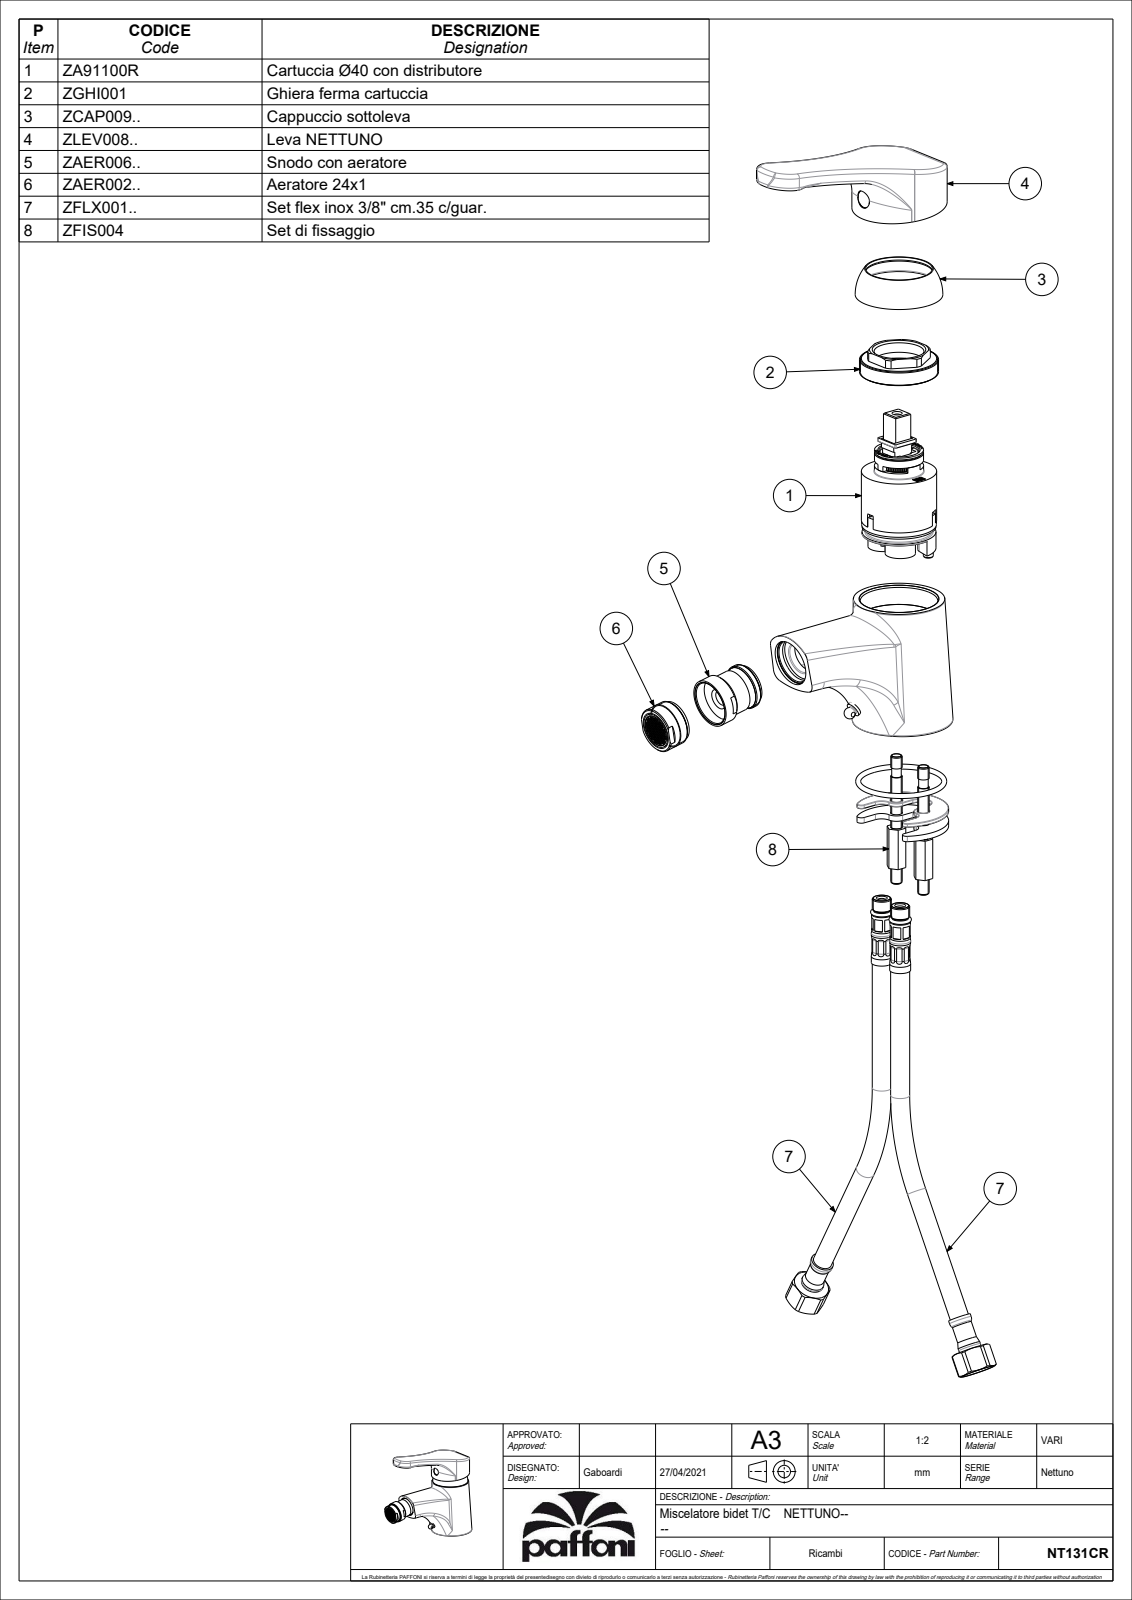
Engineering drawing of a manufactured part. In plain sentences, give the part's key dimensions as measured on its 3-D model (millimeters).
The part is named "NT131CR". Its 3-D file was written by "CREO PARAMETRIC BY PTC INC, 2020044 (CONFIG_CONTROL_DESIGN)". It is 2 solids with 2753 faces: 2010 planar, 395 cylindrical and 348 other. Overall it measures 133.44 by 118.74 by 52.85 millimeters. Its volume is 158 709 cubic millimeters and its surface area 88 818 square millimeters. Round holes: 5 of diameter 8, 3 of diameter 11, 2 of diameter 5.25, 2 of diameter 7, 2 of diameter 9, 2 of diameter 12, 2 of diameter 16, 2 of diameter 21, 1 of diameter 2.5, 1 of diameter 3.3, 1 of diameter 4, 1 of diameter 4.5. Round bosses or shafts: 3 of diameter 10, 2 of diameter 25.8, 2 of diameter 24, 2 of diameter 15.9, 2 of diameter 9.4, 2 of diameter 8, 1 of diameter 50, 1 of diameter 41.7. Partial cylindrical surfaces (rounded edges, fillets, slot ends): 51 of radius 0.5, 24 of radius 0.2, 9 of radius 2, 5 of radius 1, 4 of radius 0.3, 4 of radius 1.5, 3 of radius 5, 3 of radius 9. The main face-to-face distances are 2, 3.7, 1, 13, 5, 1.5, 15, 3.5, 4.5, 4. The hole center spacings are 13.12, 9.9, 0.71, 1.58, 2, 8.6, 8.81, 9.3.
